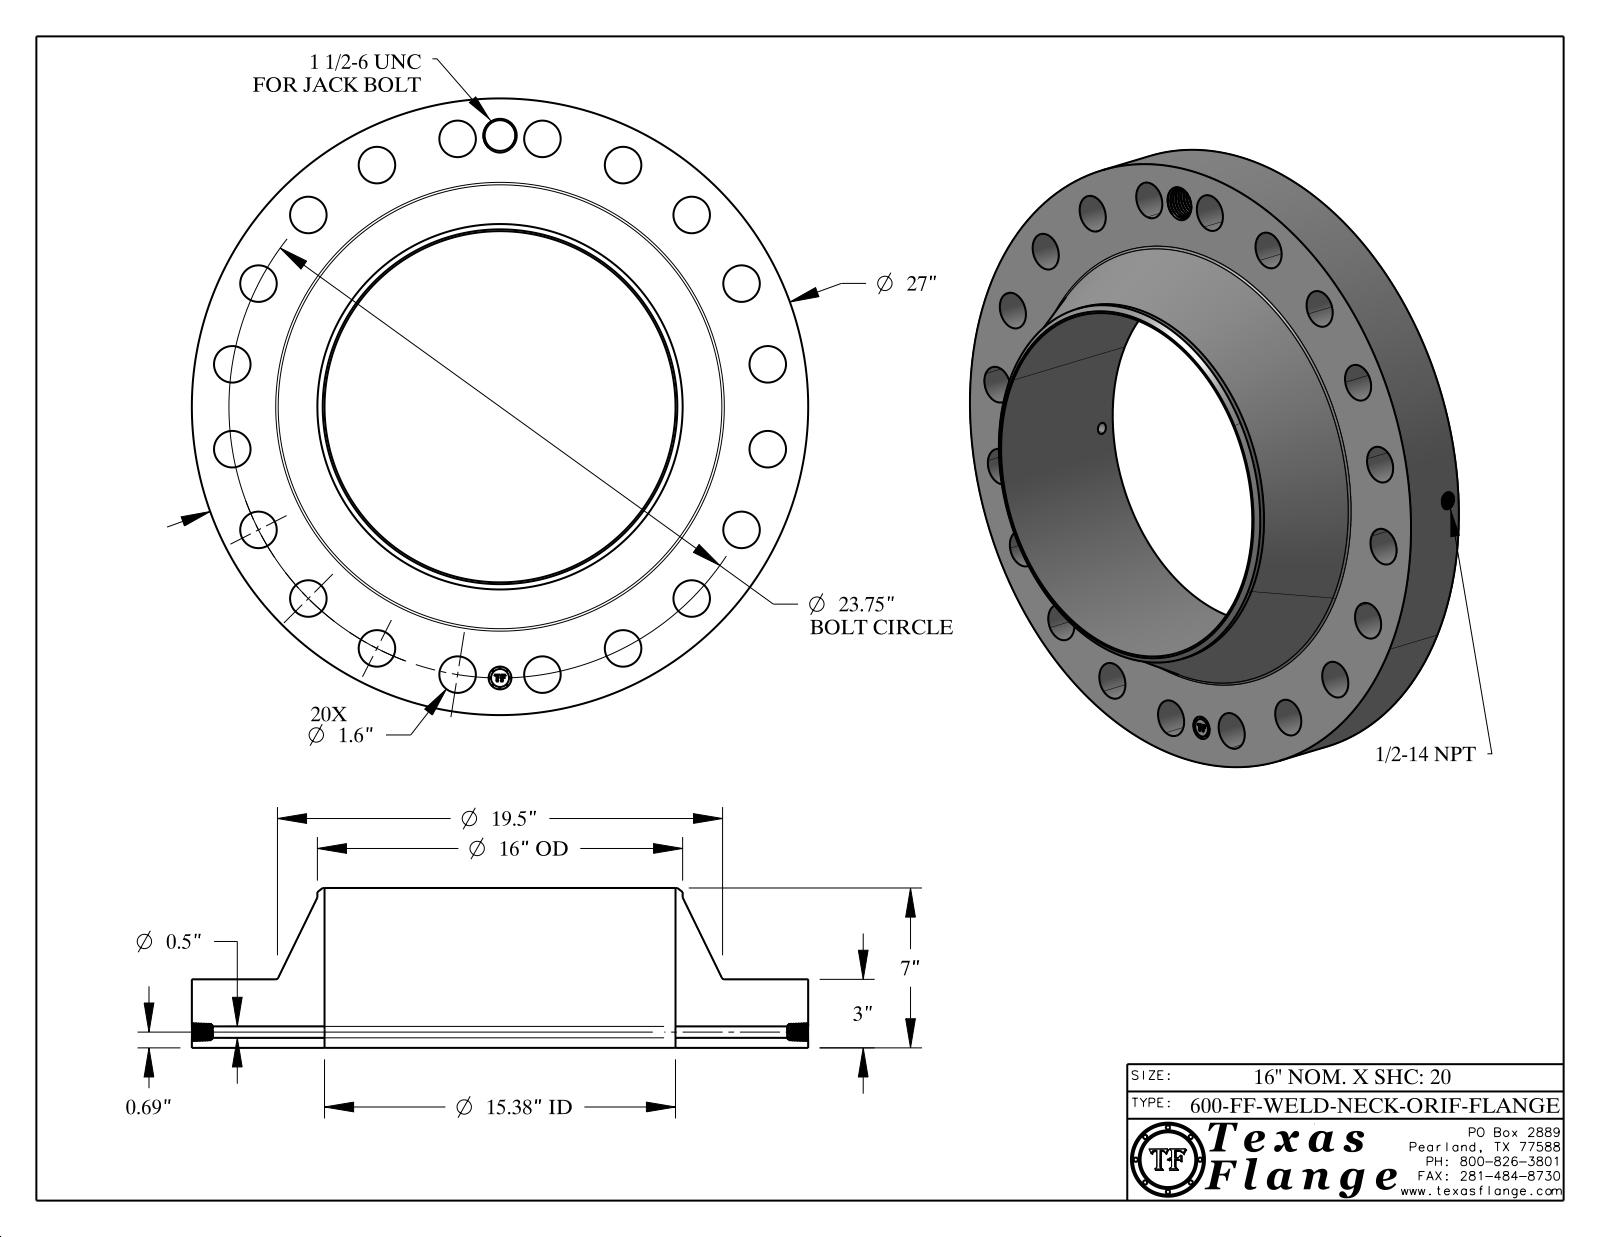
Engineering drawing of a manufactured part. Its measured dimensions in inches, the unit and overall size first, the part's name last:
Units: inches
Overall size (bounding box): 27 × 27 × 7
Round holes (diameter × count): ⌀1.6 ×20, ⌀0.5 ×1, ⌀0.672 ×1, ⌀1 ×1, ⌀1.344 ×1, ⌀15.376 ×1
Round bosses / shafts (diameter × count): ⌀0.061 ×8, ⌀27 ×1, ⌀16 ×1, ⌀0.788 ×1
Main face-to-face distances: 3, 7, 4, 0.015, 2.985, 4.015, 0.298, 0.292, 0.054, 0.248
Hole centre spacings: 11.875, 16.794, 22.587, 23.457, 3.715, 13.96, 19.214, 7.339
Volume: 1 262 in³ · Surface area: 1 763 in²
Bodies: 1 solid, 808 faces (368 planar, 122 cylindrical, 318 other)
Part name (STEP PRODUCT): 600-FF-WELD-NECK
STEP written by: CATIA V5 STEP AP214 (AUTOMOTIVE_DESIGN)
